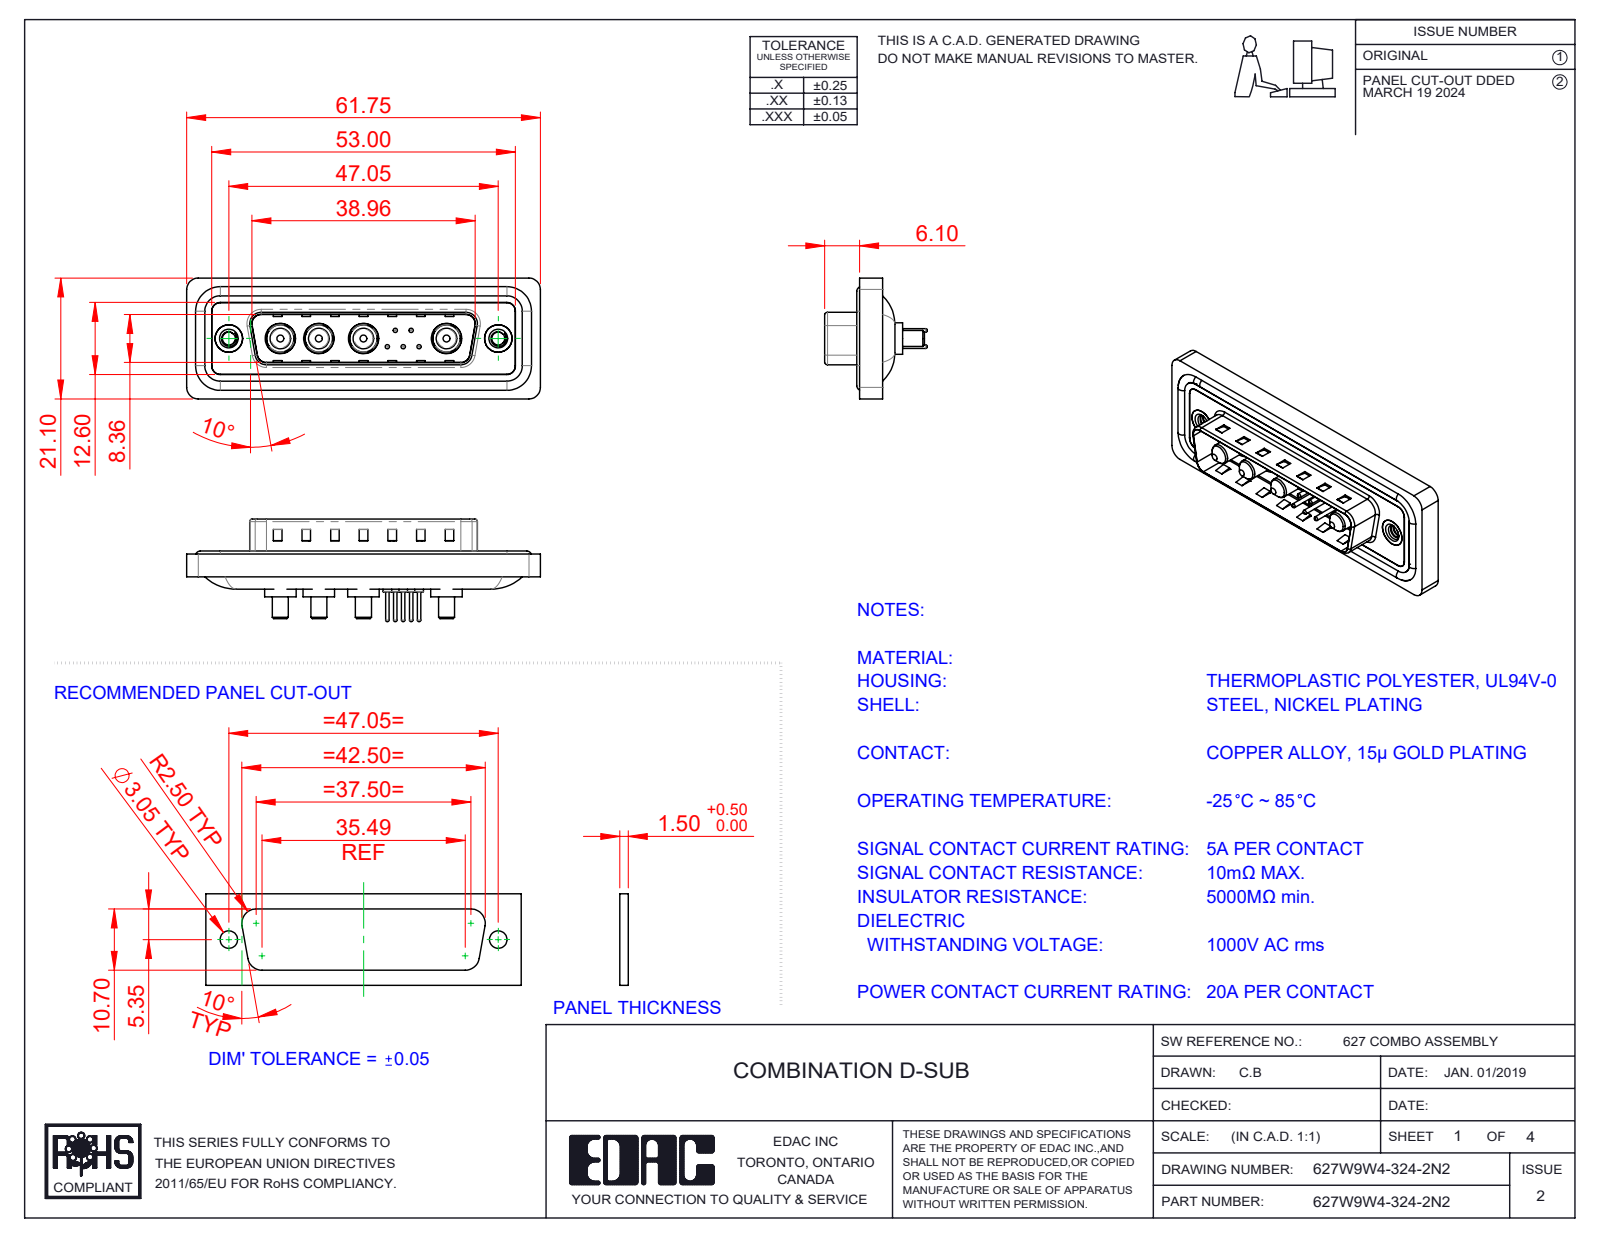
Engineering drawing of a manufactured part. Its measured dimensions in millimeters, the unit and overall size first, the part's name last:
Units: millimetres
Overall size (bounding box): 61.75 × 21.1 × 17.9
Round holes (diameter × count): ⌀0.75 ×5, ⌀1.6 ×5, ⌀2 ×5, ⌀4.85 ×4, ⌀5.3 ×4, ⌀2.26 ×2, ⌀4 ×2, ⌀4.8 ×2, ⌀5 ×2
Round bosses / shafts (diameter × count): ⌀1.5 ×5, ⌀0.6 ×5, ⌀5.5 ×4, ⌀5.2 ×4, ⌀4.75 ×4, ⌀3.75 ×4, ⌀3.6 ×4, ⌀2.8 ×4
Partial cylindrical surfaces — rounded edges, fillets, slot ends (radius × count): R1.5 ×22, R2 ×18, R0.5 ×8, R1.6 ×8, R0.25 ×4, R0.6 ×4, R0.65 ×4, R0.9 ×4
Main face-to-face distances: 0.4, 1.5, 1.1, 0.5, 1.6, 3.1, 2.9, 0.82, 9.58, 5.65
Hole centre spacings: 3.16, 2.77, 5.04, 14.51, 2.78, 4.4, 4.41, 5
Volume: 7 404 mm³ · Surface area: 11 835 mm²
Bodies: 20 solids, 824 faces (284 planar, 334 cylindrical, 206 other)
Part name (STEP PRODUCT): 627Combo Contact Row 1_24; 627Combo Shell Front_25 Contacts; 627Combo Contact Row 2_24; 627Combo Waterproof Housing_25 Contacts (+5 more)
STEP written by: SolidWorks 2023 (CONFIG_CONTROL_DESIGN)
